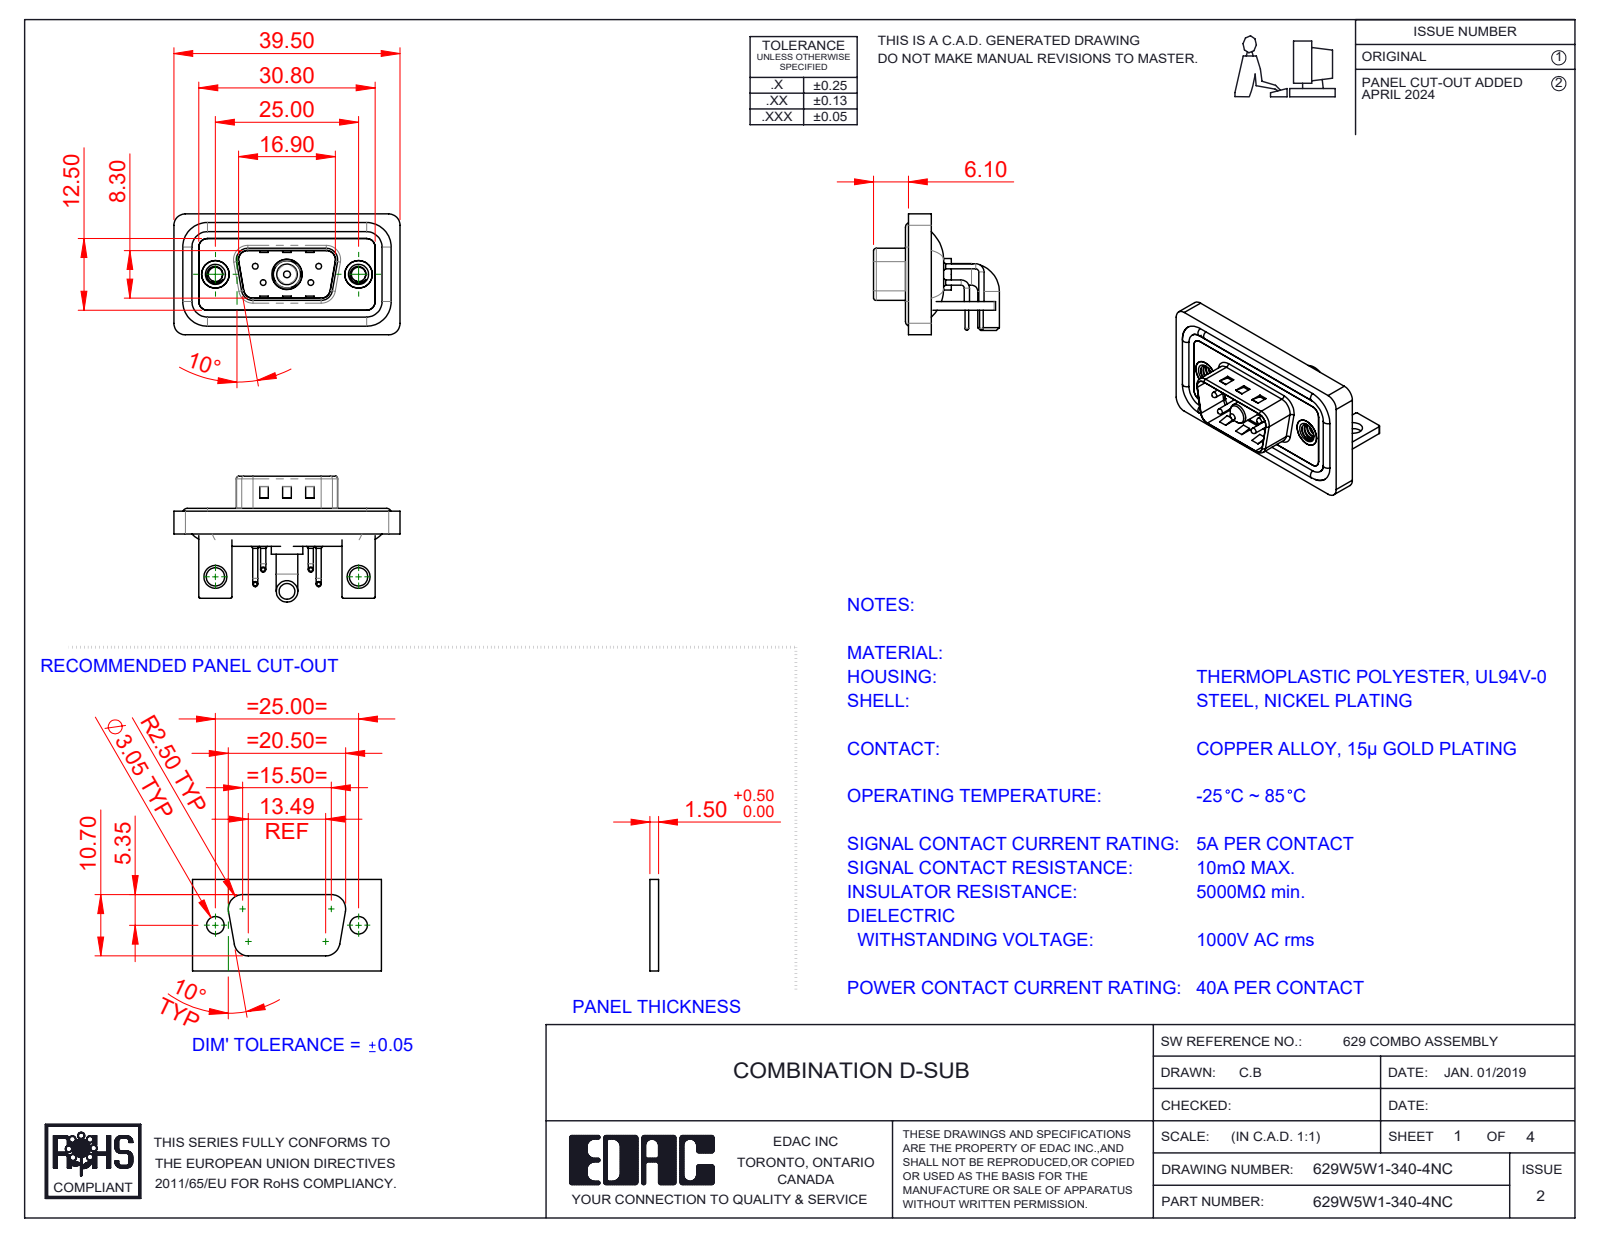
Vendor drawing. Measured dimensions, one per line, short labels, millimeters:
name: 629Combo Shell Rear_09 Contacts; 629Combo Threaded Rivet_B; 629Combo Shell Front_09 Contacts; Power Pin_40A RA (+6 more)
written by: SolidWorks 2023 (CONFIG_CONTROL_DESIGN)
unit: mm
bodies: 15 solids, 932 faces (431 planar, 363 cylindrical, 138 other)
size: 39.5 × 21.98 × 21.1
volume: 4 821 mm³; area: 7 796 mm²
holes: 4× ⌀0.75, 4× ⌀1.6, 4× ⌀2, 2× ⌀2.5, 2× ⌀3.2, 2× ⌀4, 2× ⌀4.8, 2× ⌀5, 1× ⌀4.85, 1× ⌀5.3
bosses: 8× ⌀0.9, 4× ⌀1.6, 4× ⌀1.5, 4× ⌀1, 4× ⌀0.65, 2× ⌀4.9, 2× ⌀3.75, 1× ⌀5.5
rounds: 19× R2, 18× R1.5, 16× R0.25, 9× R0.5, 8× R1.6, 4× R0.6, 4× R0.65, 4× R0.9
face distances: 0.4, 1.5, 0.8, 2.9, 1.1, 2.1, 1.2, 1.6, 2.5, 3.7
hole spacings: 3.16, 5.72, 7.1, 12.5, 18.1, 25, 4.39, 4.4
